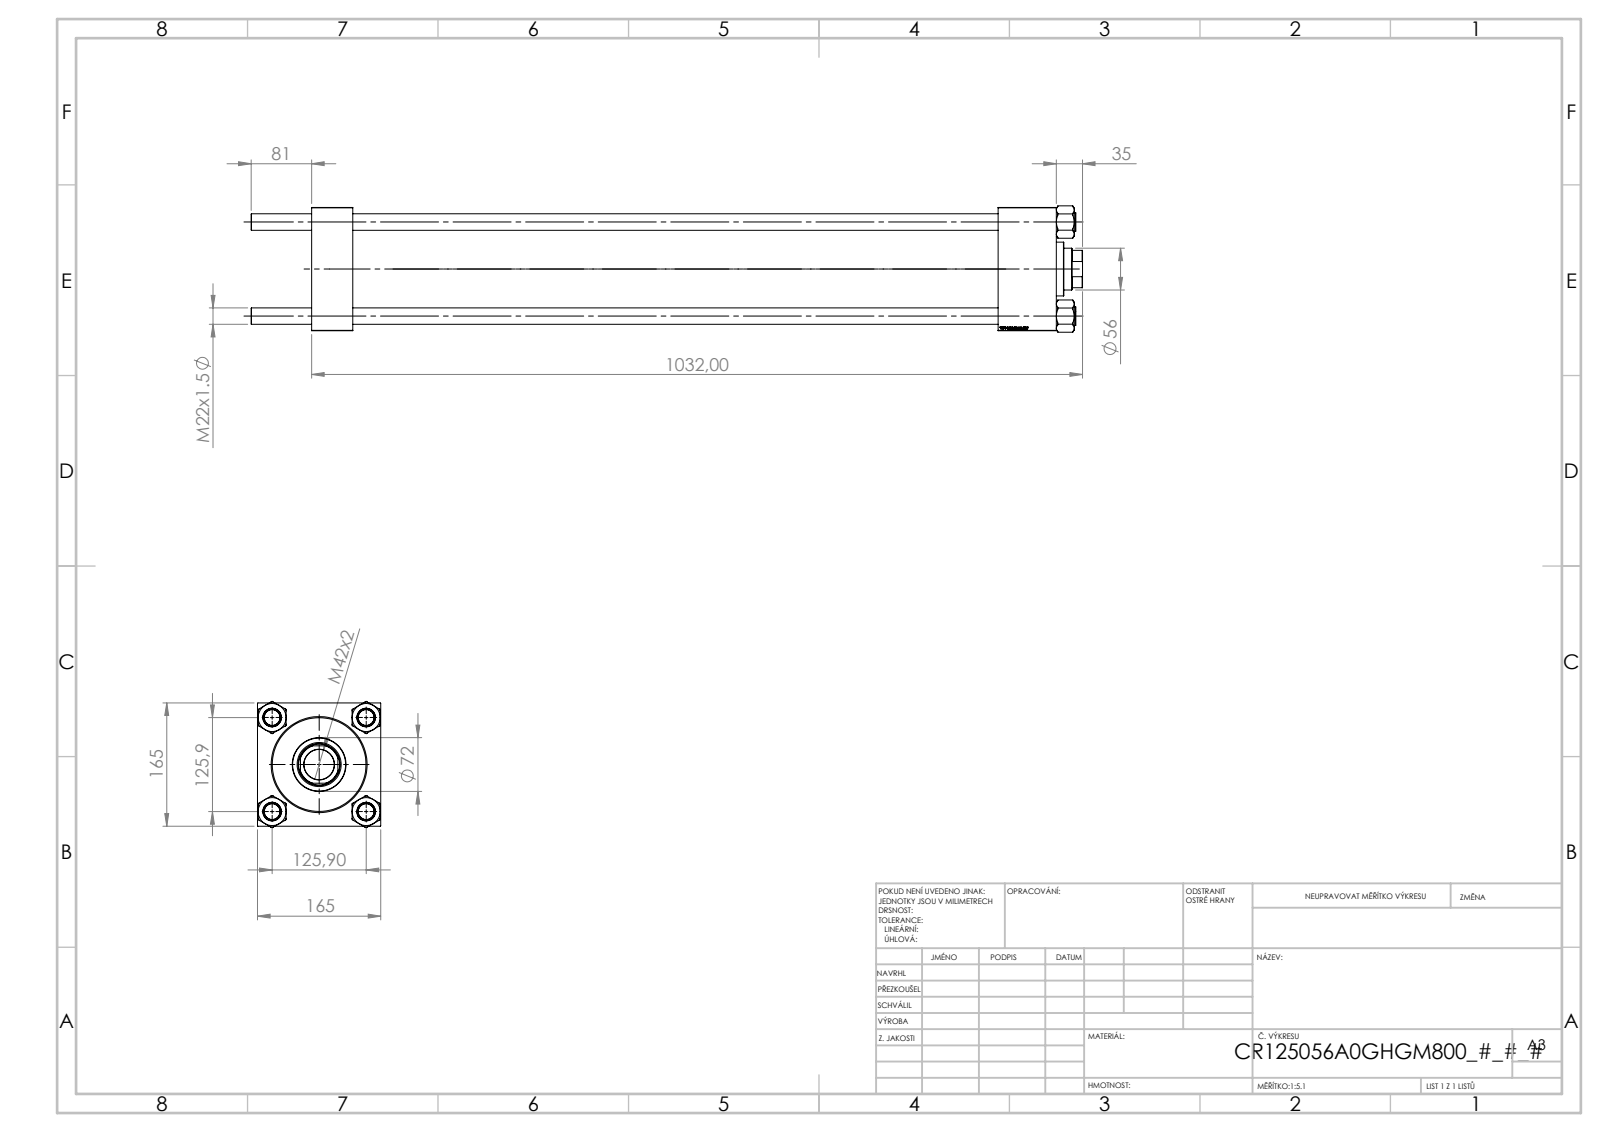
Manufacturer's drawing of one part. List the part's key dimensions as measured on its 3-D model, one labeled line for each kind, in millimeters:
Part name (STEP PRODUCT): V215_VC_A; V215CR_BODY_A; V215CR_VCP; NUT_M5 (+1 more)
STEP written by: SolidWorks 2019 (CONFIG_CONTROL_DESIGN)
Units: millimetres
Bodies: 11 solids, 1182 faces (568 planar, 78 cylindrical, 536 other)
Overall size (bounding box): 1113 × 169.14 × 165
Volume: 8 729 000 mm³ · Surface area: 1 529 000 mm²
Round holes (diameter × count): ⌀22 ×4, ⌀7 ×2, ⌀32.24 ×2, ⌀45 ×2, ⌀40.5 ×1, ⌀56 ×1, ⌀59 ×1, ⌀96 ×1, ⌀125 ×1, ⌀125.5 ×1
Round bosses / shafts (diameter × count): ⌀25 ×4, ⌀131 ×1, ⌀72 ×1
Partial cylindrical surfaces — rounded edges, fillets, slot ends (radius × count): R27 ×1
Main face-to-face distances: 165, 55, 997, 942, 919, 864, 78, 968.3, 913.3, 49.3
Hole centre spacings: 89.02, 125.9, 178.05, 918.5
